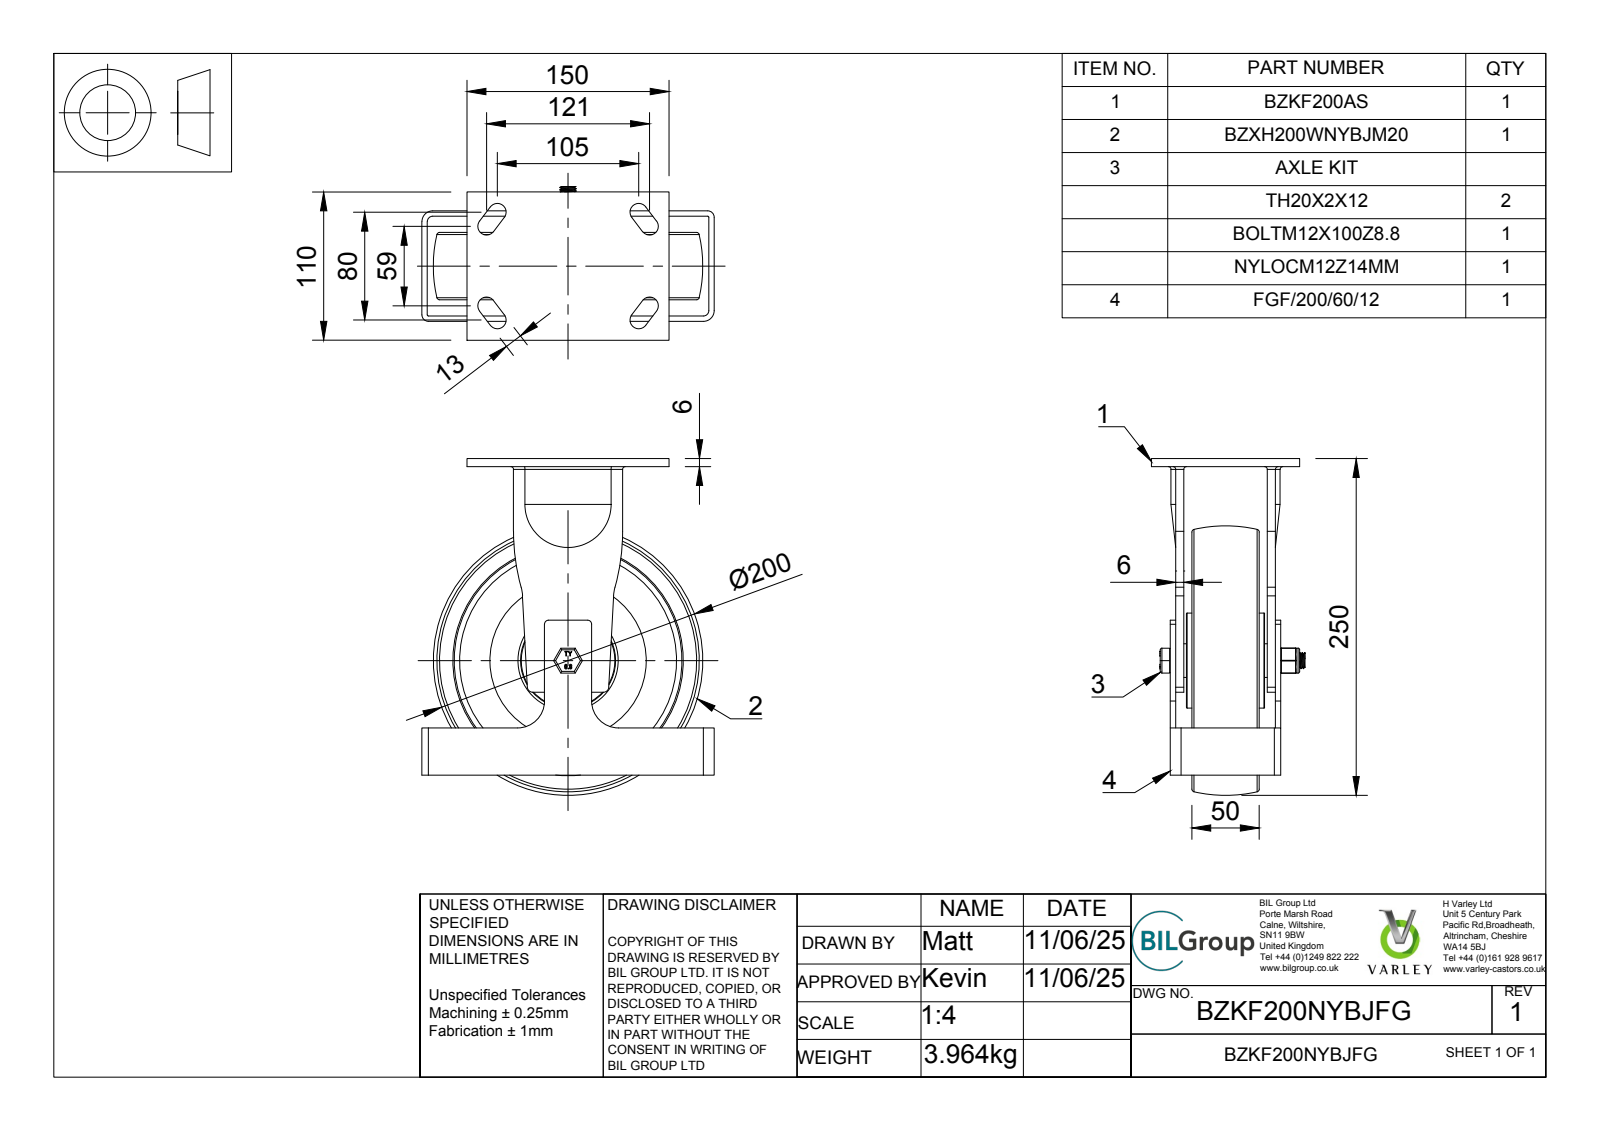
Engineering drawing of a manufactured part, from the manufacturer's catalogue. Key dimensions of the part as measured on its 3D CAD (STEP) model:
Part name (STEP PRODUCT): BZKF200NYBJFG v2; BZXH200WNYBJM20 v1; BZXH200WNYBJ; WHITE NYLON WHEEL (+8 more)
STEP written by: Autodesk Translation Framework v14.10.0.0 (AUTOMOTIVE_DESIGN)
Units: millimetres
Bodies: 35 solids, 1114 faces (402 planar, 293 cylindrical, 419 other)
Overall size (bounding box): 250 × 217 × 114
Volume: 1 251 000 mm³ · Surface area: 316 421 mm²
Round holes (diameter × count): ⌀12 ×1, ⌀12.2 ×1, ⌀13 ×1, ⌀14 ×1, ⌀20 ×1, ⌀21.5 ×1, ⌀28.5 ×1, ⌀30.8 ×1, ⌀40.3 ×1, ⌀40.5 ×1, ⌀42 ×1, ⌀47 ×1
Round bosses / shafts (diameter × count): ⌀70.5 ×1, ⌀40.8 ×1, ⌀39 ×1, ⌀31.3 ×1, ⌀27 ×1, ⌀25.4 ×1, ⌀25 ×1, ⌀19.8 ×1
Partial cylindrical surfaces — rounded edges, fillets, slot ends (radius × count): R0.5 ×18, R6.5 ×8, R1.25 ×6, R2 ×6, R4 ×4, R0.8 ×2, R3 ×2, R4.8 ×2
Main face-to-face distances: 6, 4, 33.5, 29.5, 44.5, 62, 78, 10, 48.5, 68
